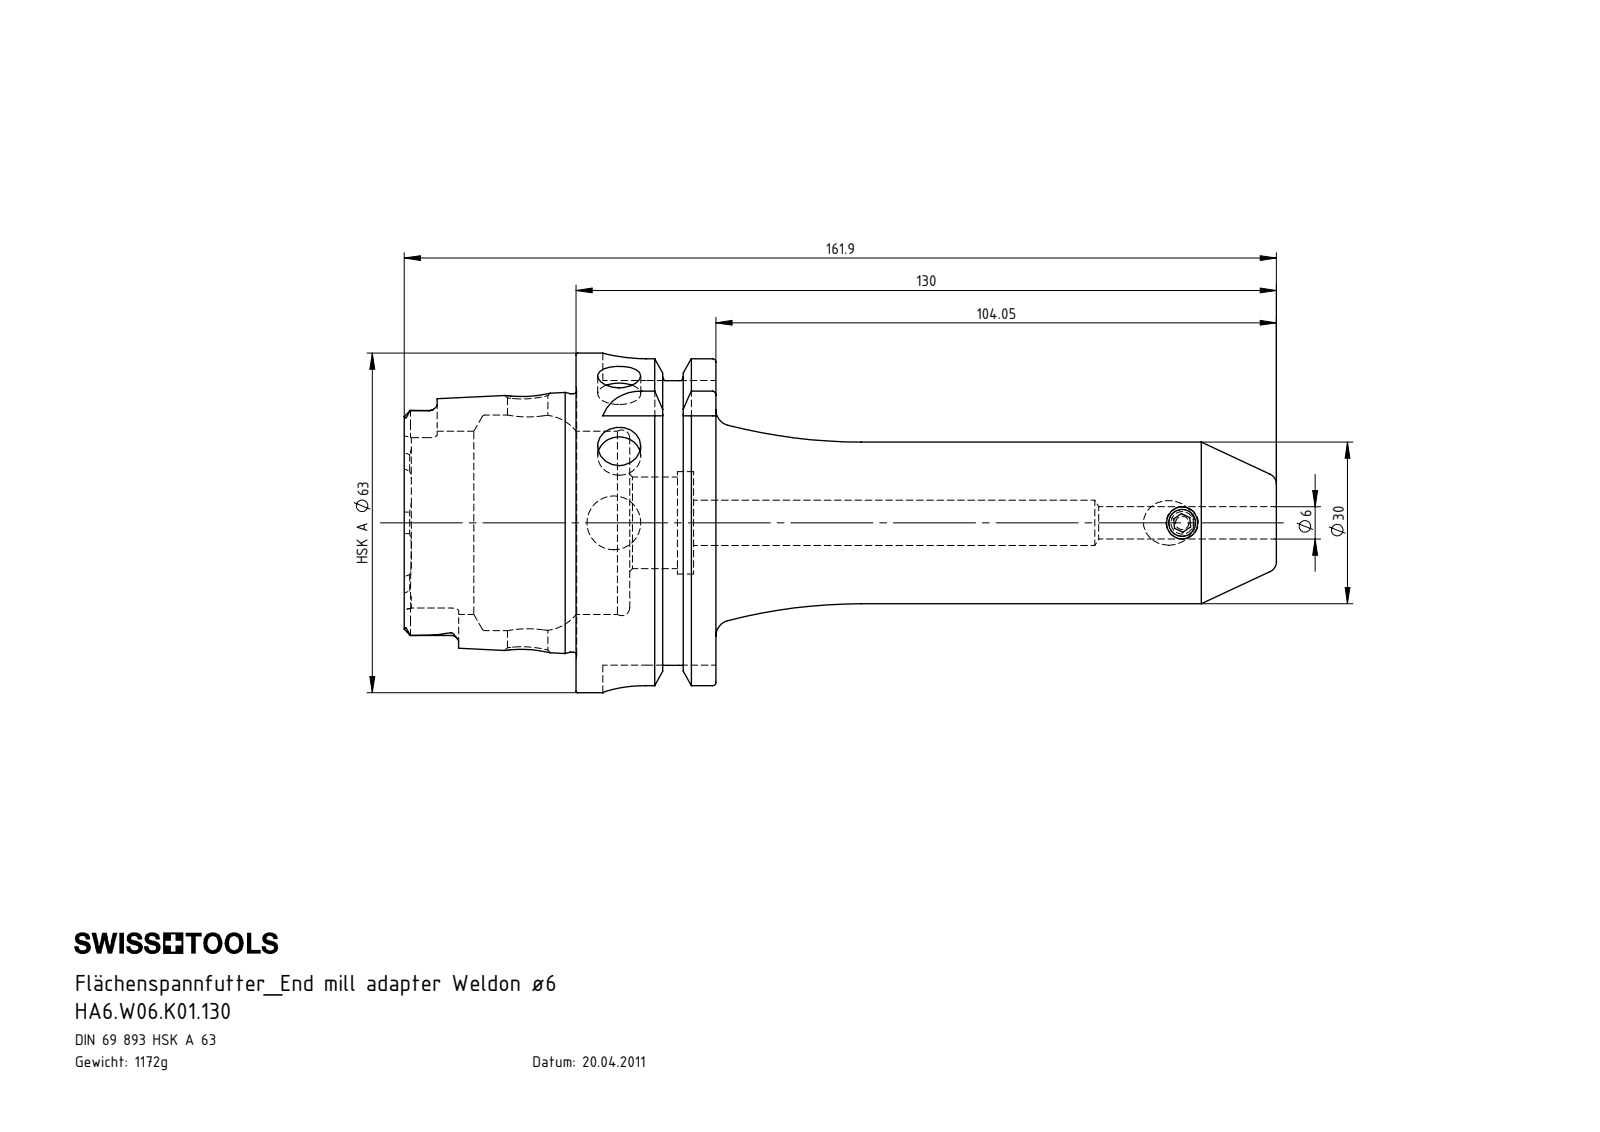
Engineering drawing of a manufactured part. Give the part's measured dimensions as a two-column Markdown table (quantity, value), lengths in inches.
| quantity | value |
| --- | --- |
| part name | HA6-W06.K01.130; W06-ER1.001.010; HA6-W06.K01.130_A_Fertigbearbeitung |
| STEP written by | SolidWorks 2012 (CONFIG_CONTROL_DESIGN) |
| units | inches |
| bodies | 2 solids, 203 faces (57 planar, 55 cylindrical, 91 other) |
| overall size | 6.374 × 2.48 × 2.48 |
| volume | 9.11 in³ |
| surface area | 53.15 in² |
| round holes (diameter × count) | 0.315 × 2, 0.197 × 1, 0.236 × 1, 0.295 × 1, 0.331 × 1, 0.394 × 1, 0.669 × 1, 0.748 × 1, 1.339 × 1, 1.575 × 1 |
| round bosses / shafts (diameter × count) | 2.48 × 1, 2.163 × 1, 1.887 × 1, 1.181 × 1, 0.236 × 1 |
| partial cylindrical surfaces (radius × count) | 0.055 × 6, 0.113 × 4, 0.315 × 4 |
| main face-to-face distances | 1.022, 0.63, 0.392, 1.256, 1.648, 2.278, 2.079, 0.858, 0.467, 2.114 |
| hole center spacings | 4.154 |
